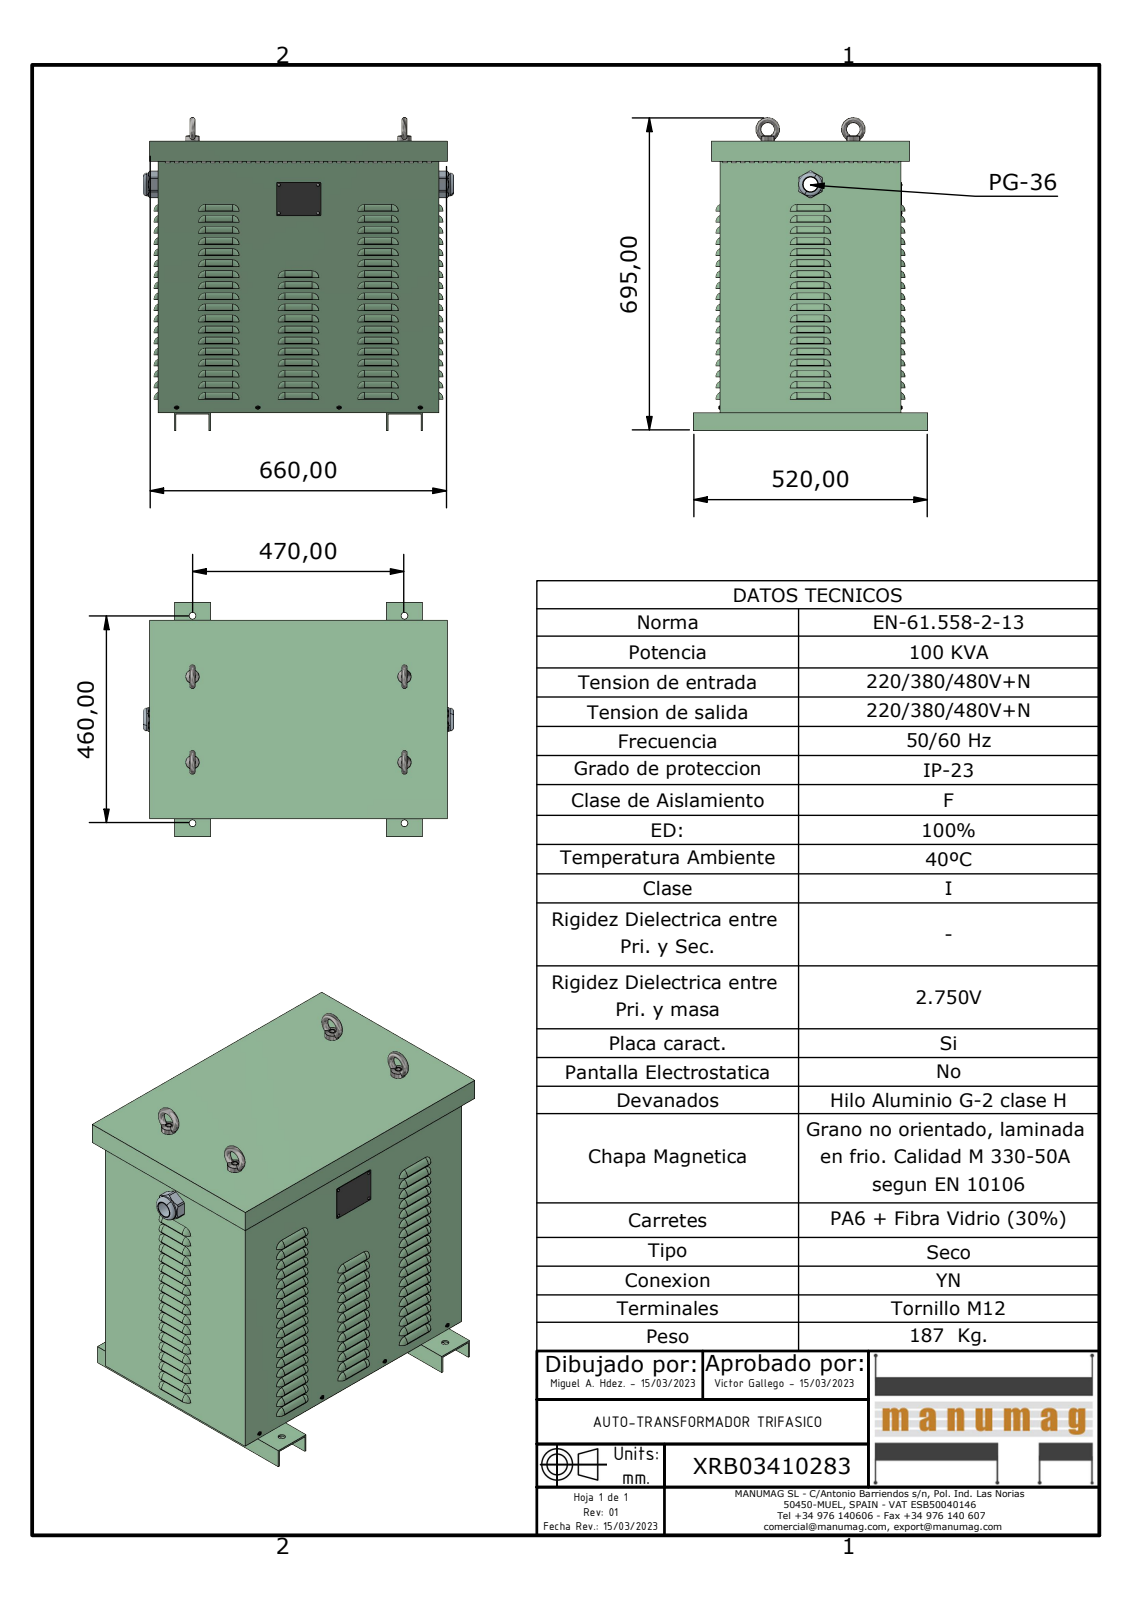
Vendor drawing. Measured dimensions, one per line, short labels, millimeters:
name: XRB03410283; JE100 CUERPO; JE100 BASE; PLACA CARACTERISTICAS (+6 more)
written by: Autodesk Inventor 2023 (AUTOMOTIVE_DESIGN)
unit: mm
bodies: 24 solids, 3065 faces (1141 planar, 1208 cylindrical, 716 other)
size: 695 × 688.2 × 520
volume: 4 880 000 mm³; area: 4 293 000 mm²
holes: 558× ⌀11, 8× ⌀15, 4× ⌀4, 4× ⌀5, 4× ⌀10.11, 1× ⌀32, 1× ⌀48
bosses: 4× ⌀30, 4× ⌀4, 4× ⌀3.62, 4× ⌀3.2, 2× ⌀51.1, 1× ⌀47.45, 1× ⌀47
rounds: 132× R14, 72× R7, 72× R15, 12× R3.88, 8× R2.5, 4× R2, 2× R30
face distances: 2, 400, 600, 621, 398, 402, 602, 619, 598, 623
hole spacings: 30, 15, 582, 582.77, 199, 45, 582.19, 583.74
